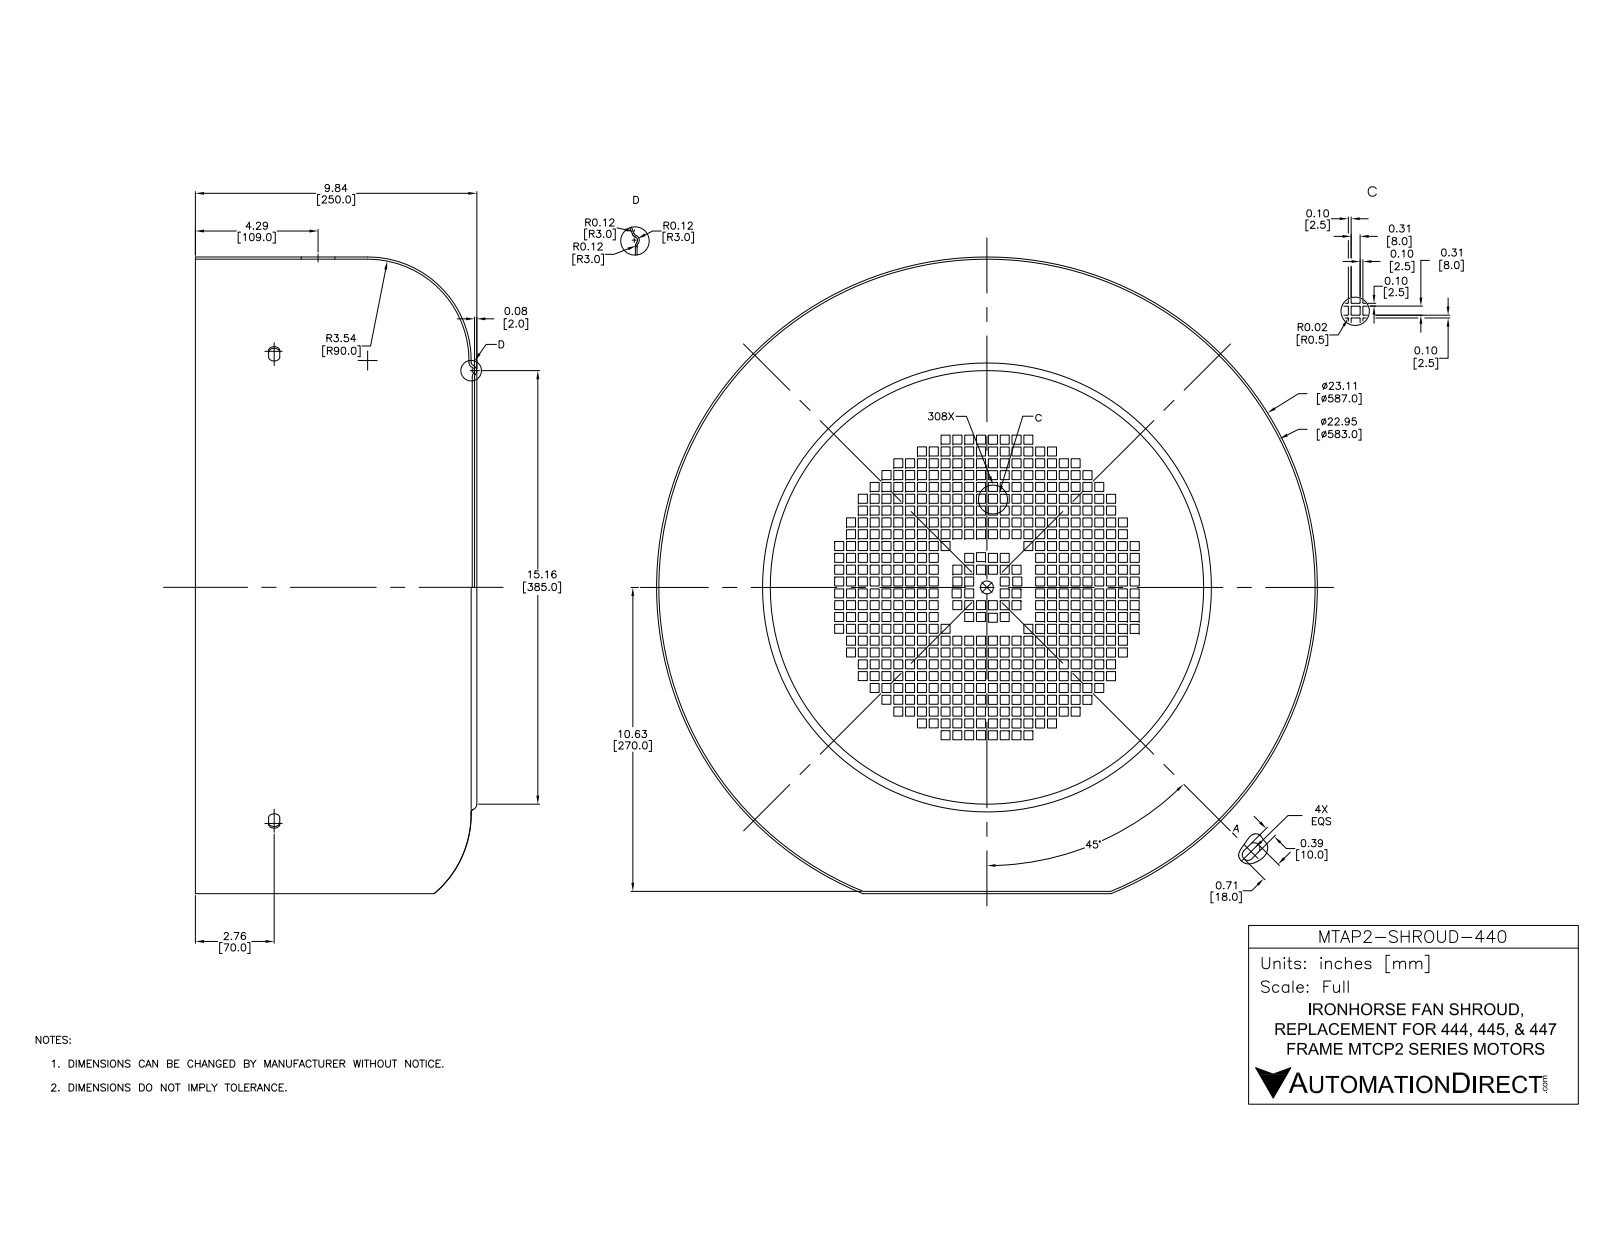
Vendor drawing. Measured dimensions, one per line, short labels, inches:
name: MTAP2-SHROUD-440
written by: SolidWorks 2017 (AUTOMOTIVE_DESIGN)
unit: in
bodies: 14 solids, 2756 faces (2624 planar, 67 cylindrical, 65 other)
size: 22.989 × 22.183 × 10.512
volume: 79.67 in³; area: 2 165 in²
holes: 4× ⌀0.331, 4× ⌀0.542, 1× ⌀0.453, 1× ⌀0.748, 1× ⌀22.713, 1× ⌀22.832
bosses: 4× ⌀0.63, 4× ⌀0.315, 1× ⌀22.989, 1× ⌀0.866, 1× ⌀0.827, 1× ⌀0.728
rounds: 8× R0.197, 1× R0.226, 1× R10.315, 1× R11.417
face distances: 0.059, 0.079, 0.02, 0.039, 9.921, 9.941, 9.98, 1.26, 8.661, 8.681
hole spacings: 10.728, 15.172, 0.322, 21.457, 10.718, 10.726, 10.731, 10.739
